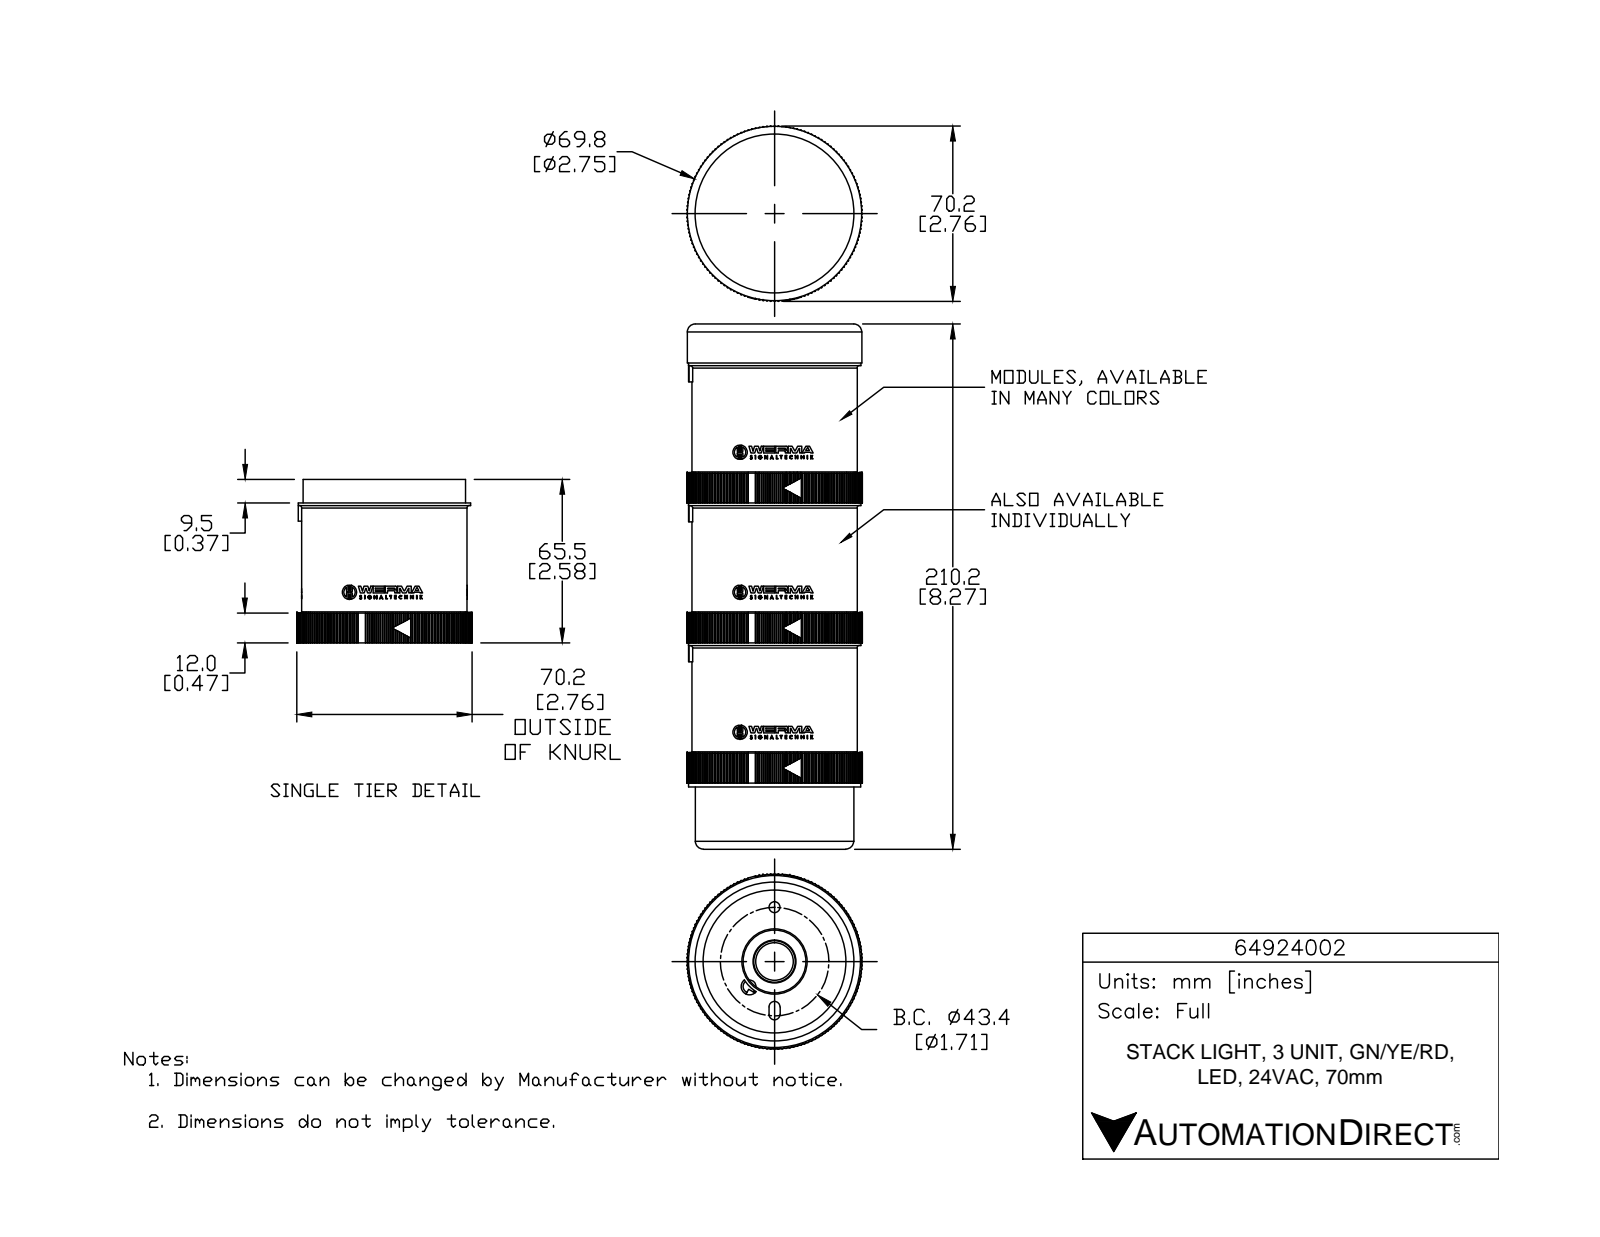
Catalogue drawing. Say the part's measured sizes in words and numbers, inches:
The part is named "64924002_BASE; 649_XXX_XX_YELLOW; 649_XXX_XX_RED; 64924002_ORING (+3 more)". Its 3-D file was written by "SolidWorks 2014 (AUTOMOTIVE_DESIGN)". It is 9 solids with 4062 faces: 2287 planar, 1705 cylindrical and 70 other. Overall it measures 8.275 by 2.762 by 2.762 inches. Its volume is 9.096 cubic inches and its surface area 291.3 square inches. Round holes: 6 of diameter 0.18, 1 of diameter 0.175, 1 of diameter 0.2, 1 of diameter 0.255, 1 of diameter 0.347, 1 of diameter 0.595, 1 of diameter 0.991, 1 of diameter 1.857, 1 of diameter 2.339, 1 of diameter 2.392, 1 of diameter 2.539, 1 of diameter 2.65. Round bosses or shafts: 1 of diameter 2.75, 1 of diameter 2.717, 1 of diameter 2.712, 1 of diameter 2.559, 1 of diameter 2.552, 1 of diameter 2.499, 1 of diameter 1.151, 1 of diameter 0.675. Partial cylindrical surfaces (rounded edges, fillets, slot ends): 285 of radius 0.008, 12 of radius 0.03, 12 of radius 0.059, 6 of radius 0.085, 6 of radius 0.105, 2 of radius 0.087, 2 of radius 0.127, 2 of radius 0.168. The main face-to-face distances are 2.205, 4.409, 0.076, 1.767, 1.769, 0.025, 1.768, 2.281, 2.129, 0.273. The hole center spacings are 0.761, 0.761, 1.319, 1.522, 0.271, 0.421, 0.435, 0.533.
